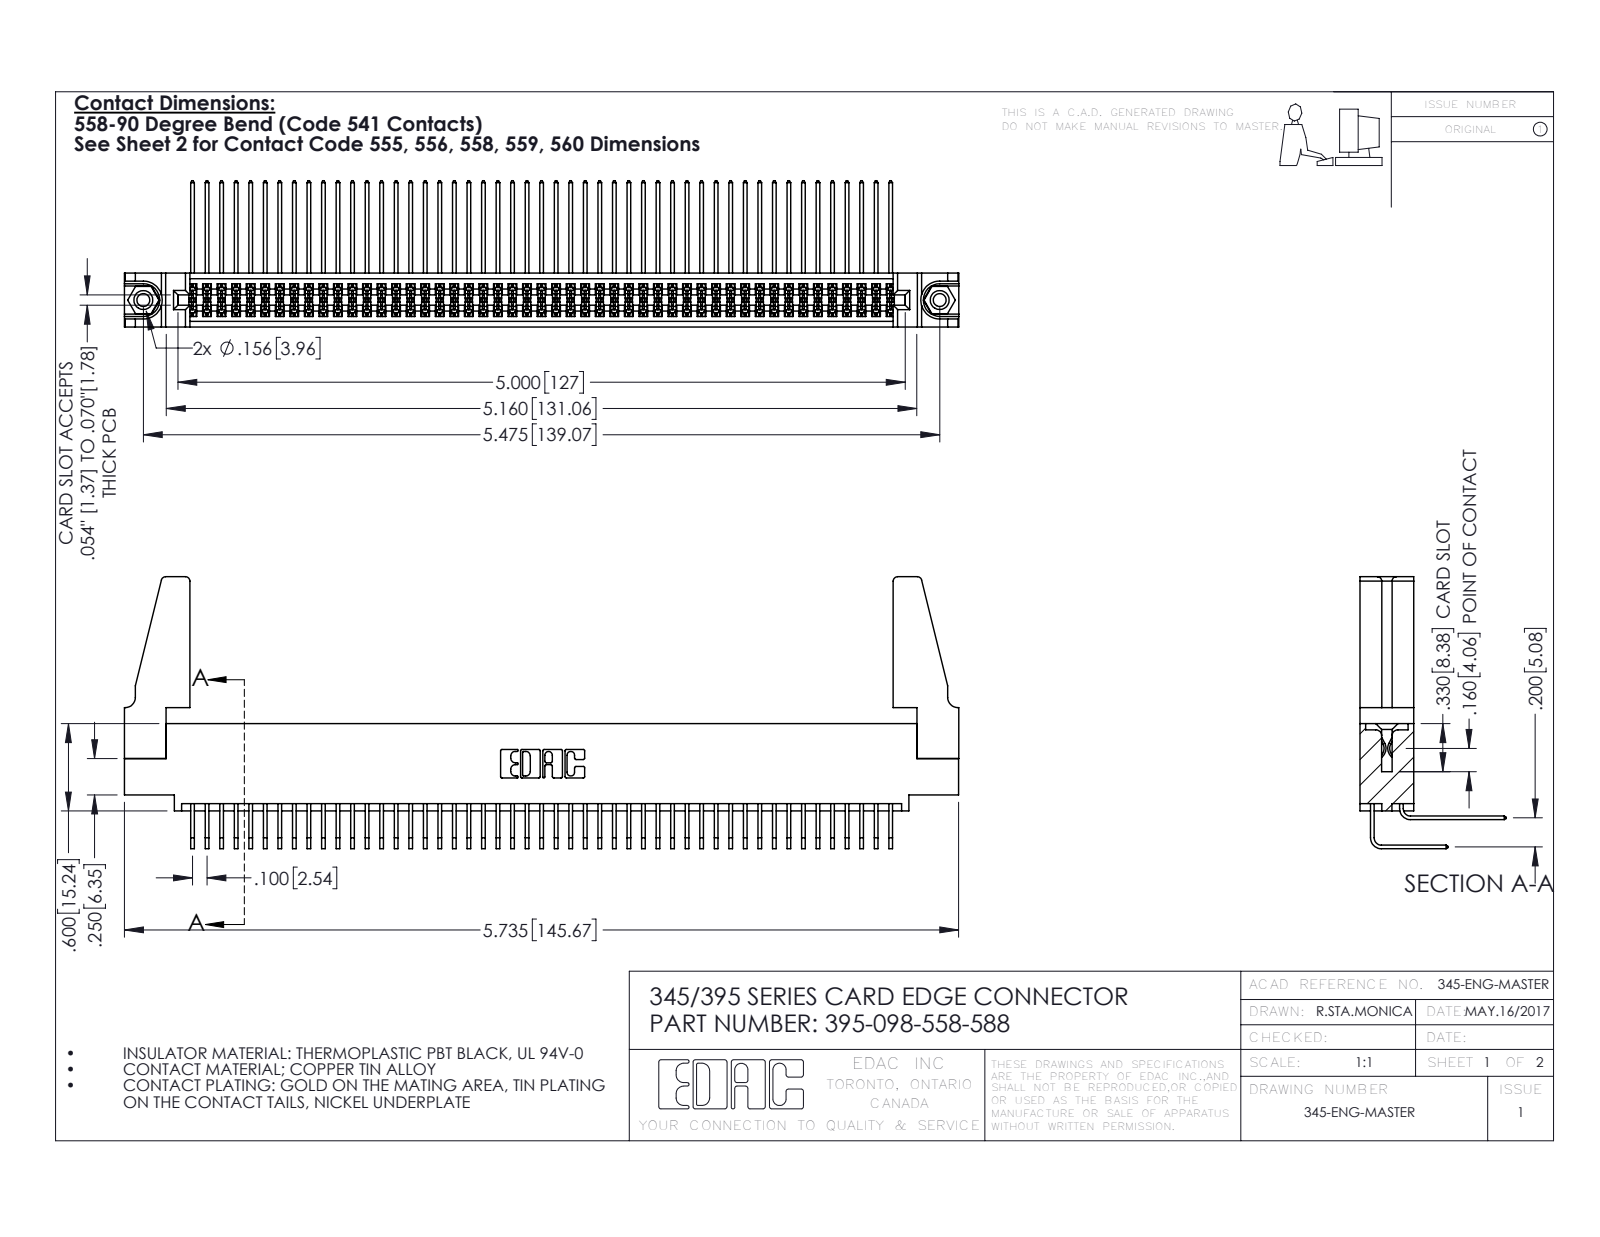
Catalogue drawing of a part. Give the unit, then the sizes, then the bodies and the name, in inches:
Units: inches
Overall size (bounding box): 5.736 × 1.869 × 1.005
Round holes (diameter × count): ⌀0.089 ×2, ⌀0.125 ×2, ⌀0.156 ×2, ⌀0.064 ×1
Round bosses / shafts (diameter × count): ⌀0.155 ×2
Partial cylindrical surfaces — rounded edges, fillets, slot ends (radius × count): R0.006 ×148, R0.01 ×22, R0.03 ×8, R0.007 ×6, R0.031 ×6, R0.026 ×3, R0.014 ×2, R0.019 ×2
Main face-to-face distances: 0.072, 0.298, 0.2, 0.37, 0.098, 0.272, 0.025, 0.225, 0.025, 0.175
Hole centre spacings: 0.27, 5.239, 5.475
Volume: 1.096 in³ · Surface area: 43.02 in²
Bodies: 103 solids, 5350 faces (3586 planar, 1748 cylindrical, 16 other)
Part name (STEP PRODUCT): 345 Part_0.110 Offset - 0.156 Dia-TH; 345-292-001_558 559 Tail - 1; 345-292-001_558 Tail - 2; 345-250-001_345-250-001-102 (+2 more)
STEP written by: SolidWorks 2016 (CONFIG_CONTROL_DESIGN)
